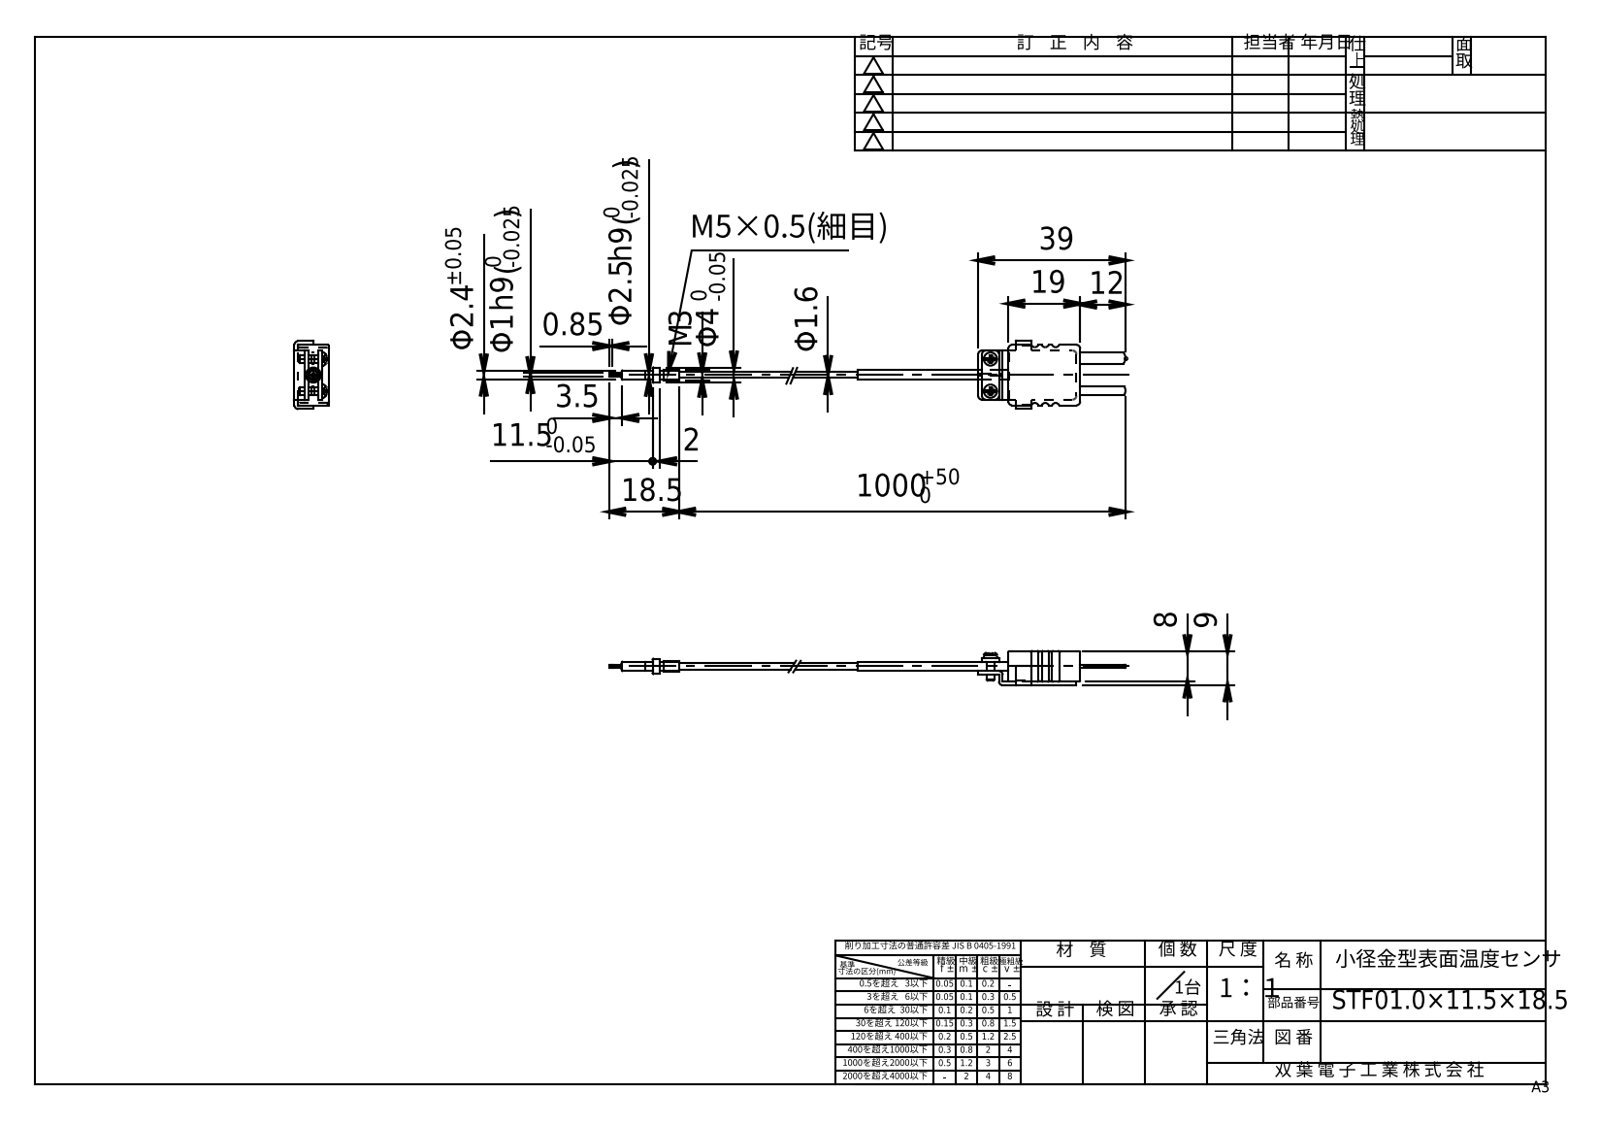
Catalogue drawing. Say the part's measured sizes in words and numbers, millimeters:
Its 3-D file was written by "XStep 1.0 (automotive_design)". It is 1 solid with 185 faces: 87 planar, 64 cylindrical and 34 other. Overall it measures 1018.5 by 18 by 9 millimeters. Its volume is 5 028 cubic millimeters and its surface area 6 956 square millimeters. Round bosses or shafts: 2 of diameter 3.5, 2 of diameter 2, 1 of diameter 4, 1 of diameter 3, 1 of diameter 2.56, 1 of diameter 2.5, 1 of diameter 2.4, 1 of diameter 2.2. Partial cylindrical surfaces (rounded edges, fillets, slot ends): 22 of radius 1, 10 of radius 0.2, 1 of radius 1.89, 1 of radius 2.2. The main face-to-face distances are 9, 1, 2.75, 6.25, 3.6, 4.4, 2.5, 3.5, 5.25, 0.85.
